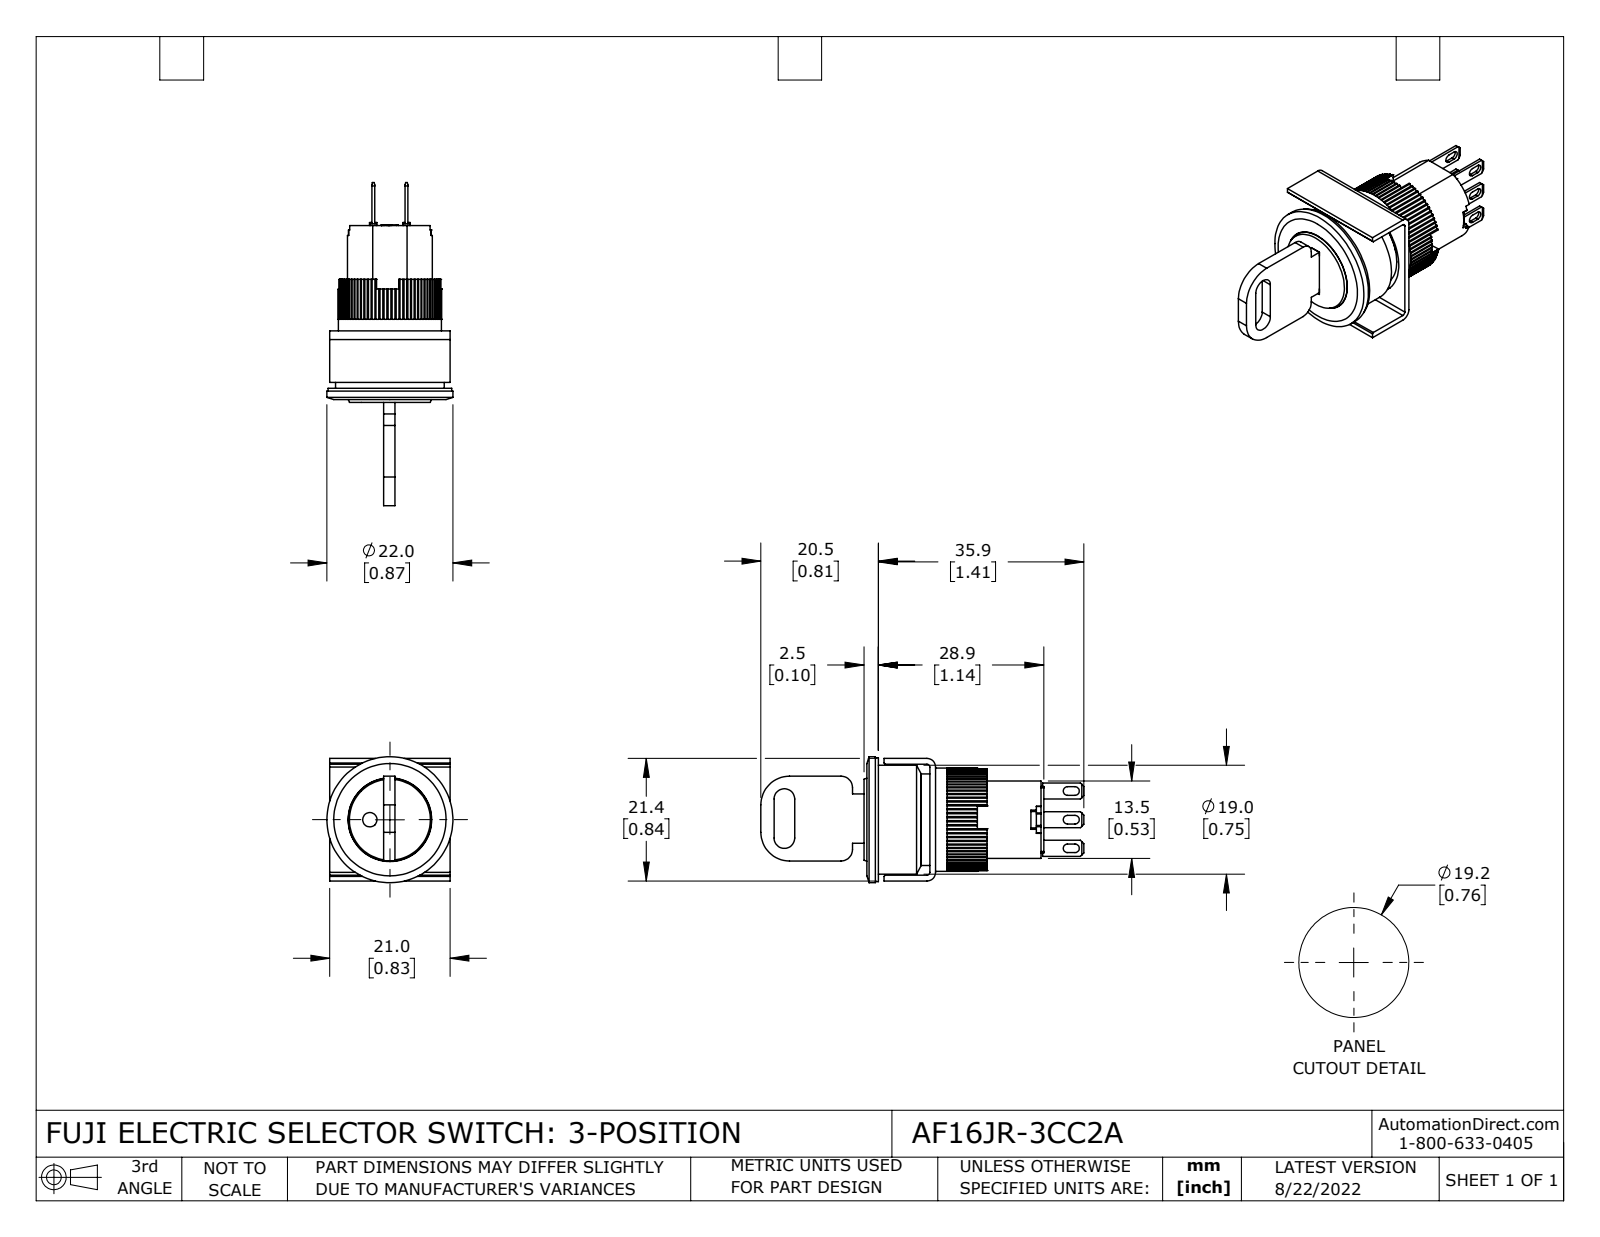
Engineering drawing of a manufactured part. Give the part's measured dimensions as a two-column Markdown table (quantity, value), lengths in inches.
| quantity | value |
| --- | --- |
| part name | AF16JR-3CC2A |
| STEP written by | SolidWorks 2021 (CONFIG_CONTROL_DESIGN) |
| units | inches |
| bodies | 13 solids, 707 faces (518 planar, 183 cylindrical, 6 other) |
| overall size | 2.22 × 0.866 × 0.866 |
| volume | 0.495 in³ |
| surface area | 11.24 in² |
| round holes (diameter × count) | 0.039 × 1, 0.098 × 1, 0.575 × 1, 0.709 × 1, 0.748 × 1 |
| round bosses / shafts (diameter × count) | 0.866 × 1, 0.85 × 1, 0.63 × 1, 0.583 × 1, 0.571 × 1 |
| partial cylindrical surfaces (radius × count) | 0.01 × 80, 0.008 × 12, 0.03 × 6, 0.02 × 2, 0.059 × 2, 0.071 × 2, 0.079 × 2, 0.197 × 2 |
| main face-to-face distances | 0.079, 0.039, 0.02, 0.374, 0.177, 0.098, 0.394, 0.803, 0.059, 0.764 |
| hole center spacings | 0.138 |
